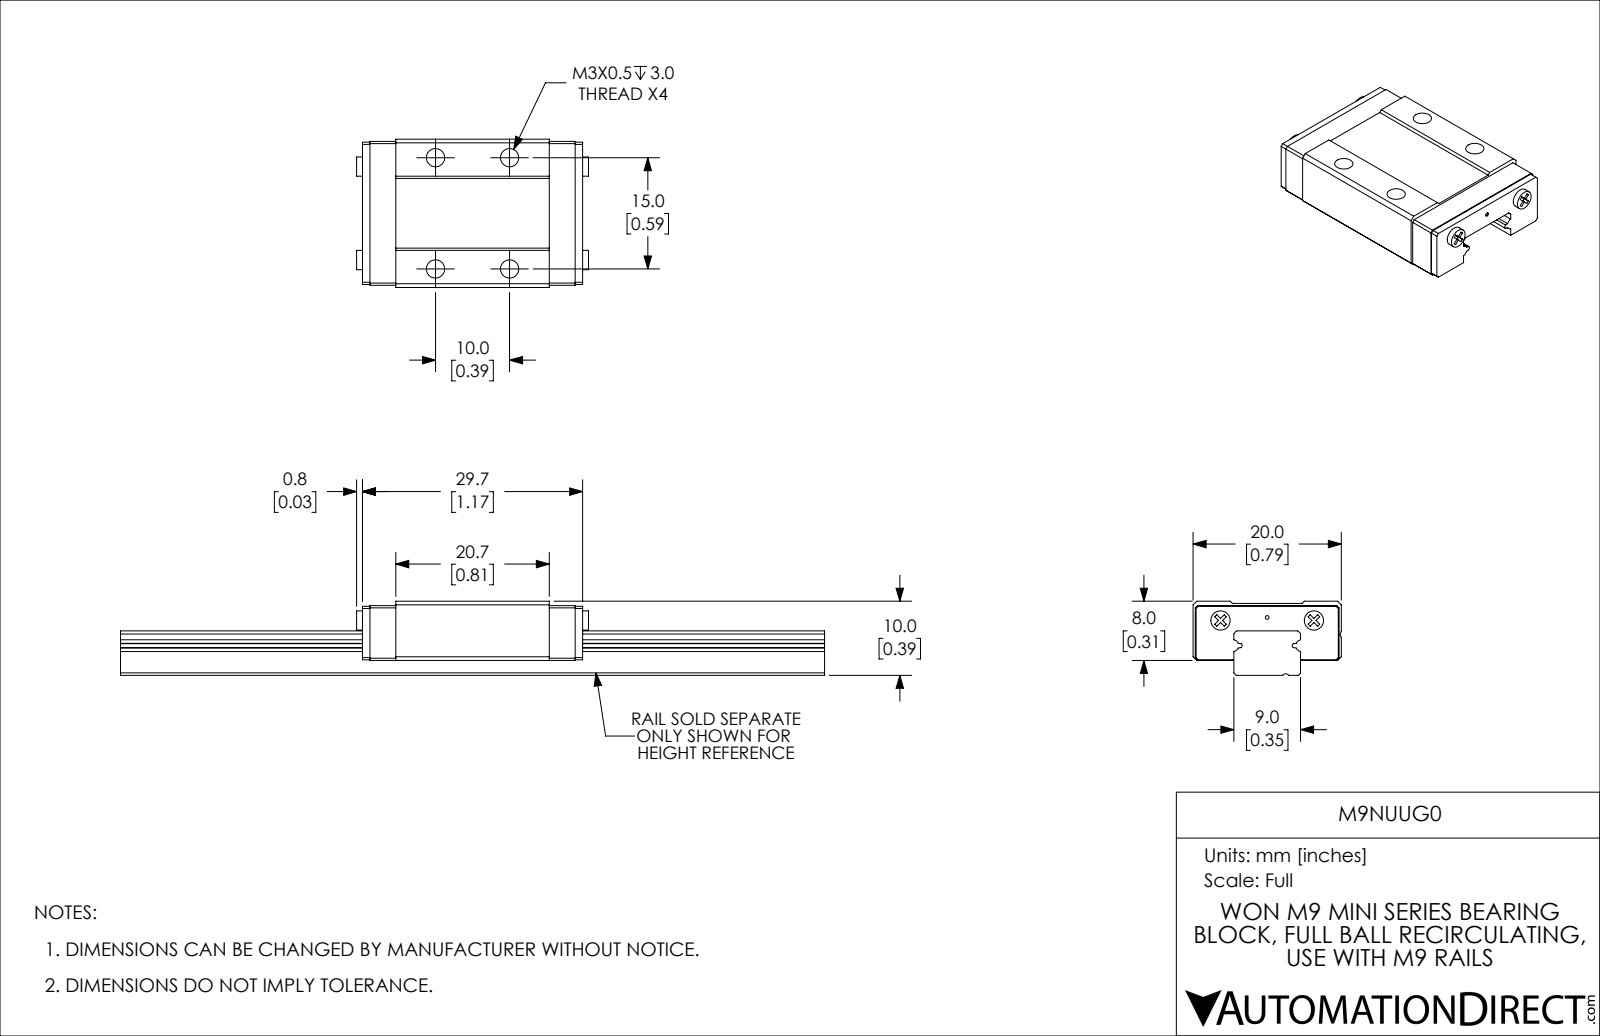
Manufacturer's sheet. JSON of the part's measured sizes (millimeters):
{"part_name": "M9NUUG0", "step_written_by": "SolidWorks 2019 (CONFIG_CONTROL_DESIGN)", "units": "millimeters", "bodies": {"solids": 1, "faces": 156, "planar": 119, "cylindrical": 29, "other": 8}, "overall_size": [31.3, 20, 8], "volume_mm3": 3467, "surface_area_mm2": 2313, "round_holes": [[2.46, 4], [0.5, 1]], "round_bosses_or_shafts": [[2.6, 2]], "partial_cylinders_radius": [[0.32, 2], [0.8, 2], [0.95, 2], [0.6, 1]], "face_to_face_distances": [4, 7.7, 3.7, 8, 7.4, 3.4, 0.6, 20, 5.5, 14.5], "hole_center_spacings": [10, 15, 18.03]}
